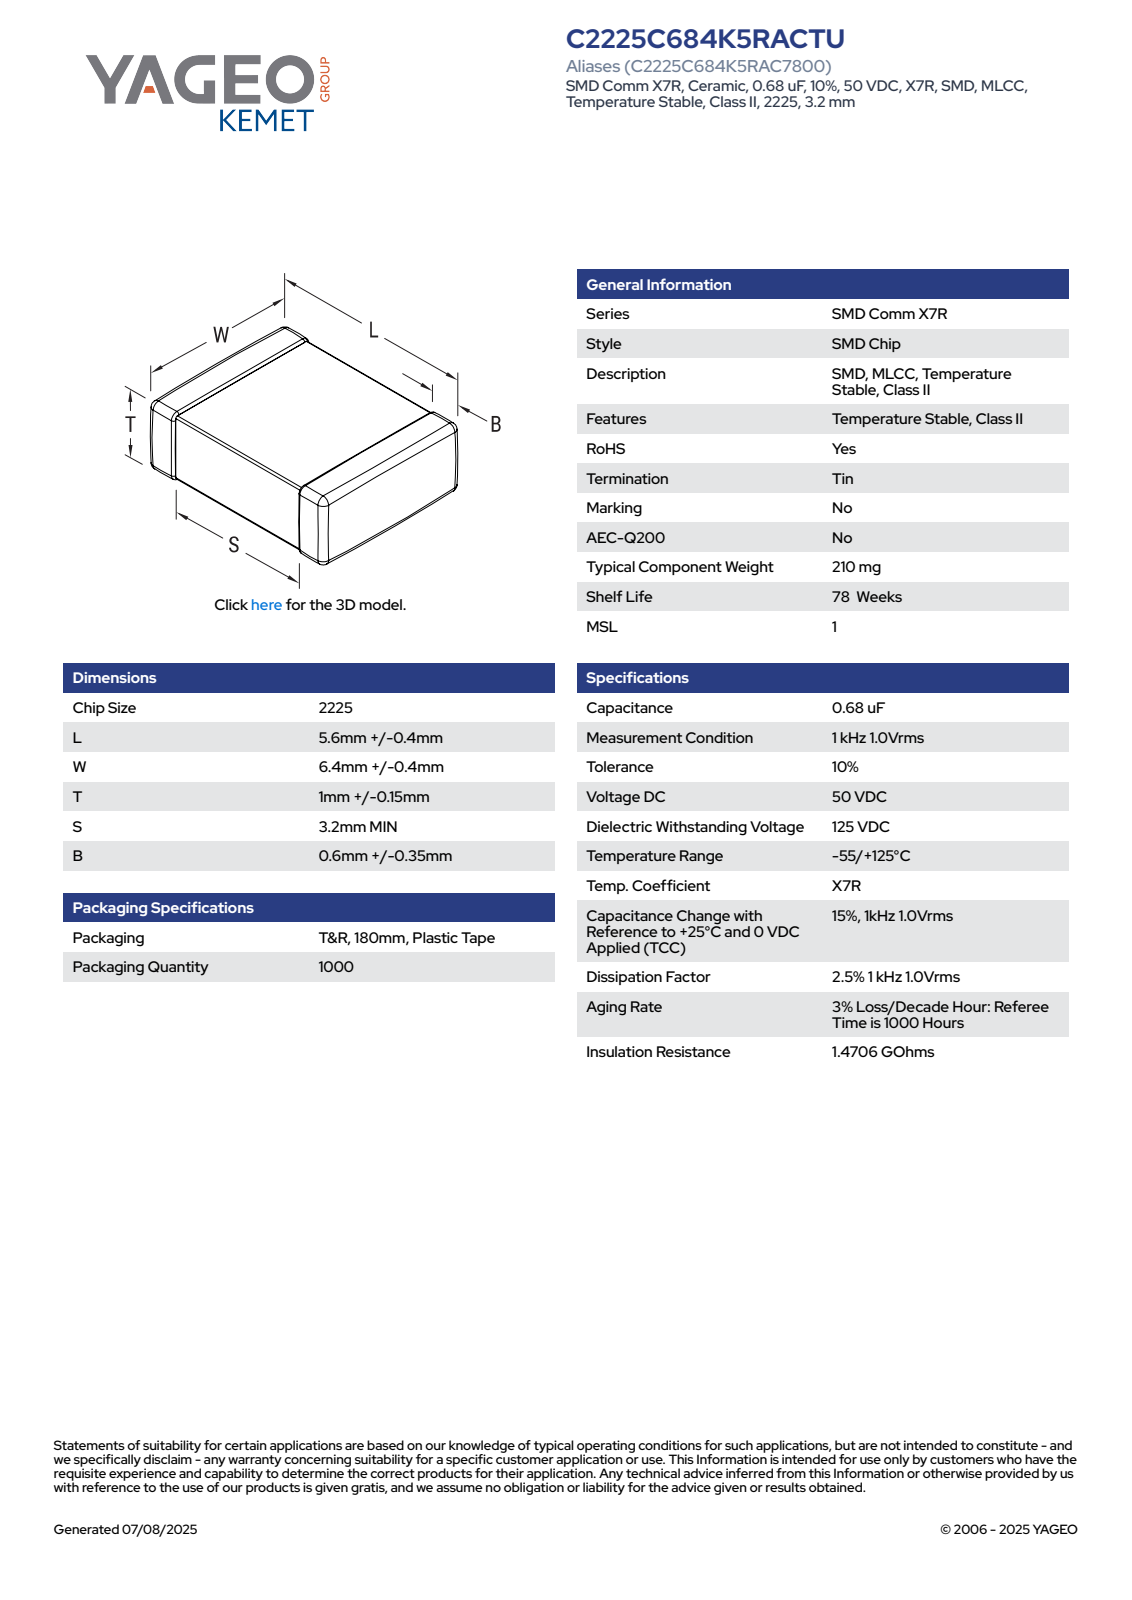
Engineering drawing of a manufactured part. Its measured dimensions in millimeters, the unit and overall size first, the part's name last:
Units: millimetres
Overall size (bounding box): 6.8 × 6 × 1.15
Partial cylindrical surfaces — rounded edges, fillets, slot ends (radius × count): R0.14 ×24
Main face-to-face distances: 0.87, 1.01, 1.15, 6, 6.52, 6.66, 6.8, 1, 2.24, 3.76
Volume: 38 mm³ · Surface area: 111 mm²
Bodies: 4 solids, 129 faces (71 planar, 42 cylindrical, 16 other)
Part name (STEP PRODUCT): CCS_CCSTD_2225_L6W6.8T1.15B0.6
STEP written by: SolidWorks 2021 (AUTOMOTIVE_DESIGN)
